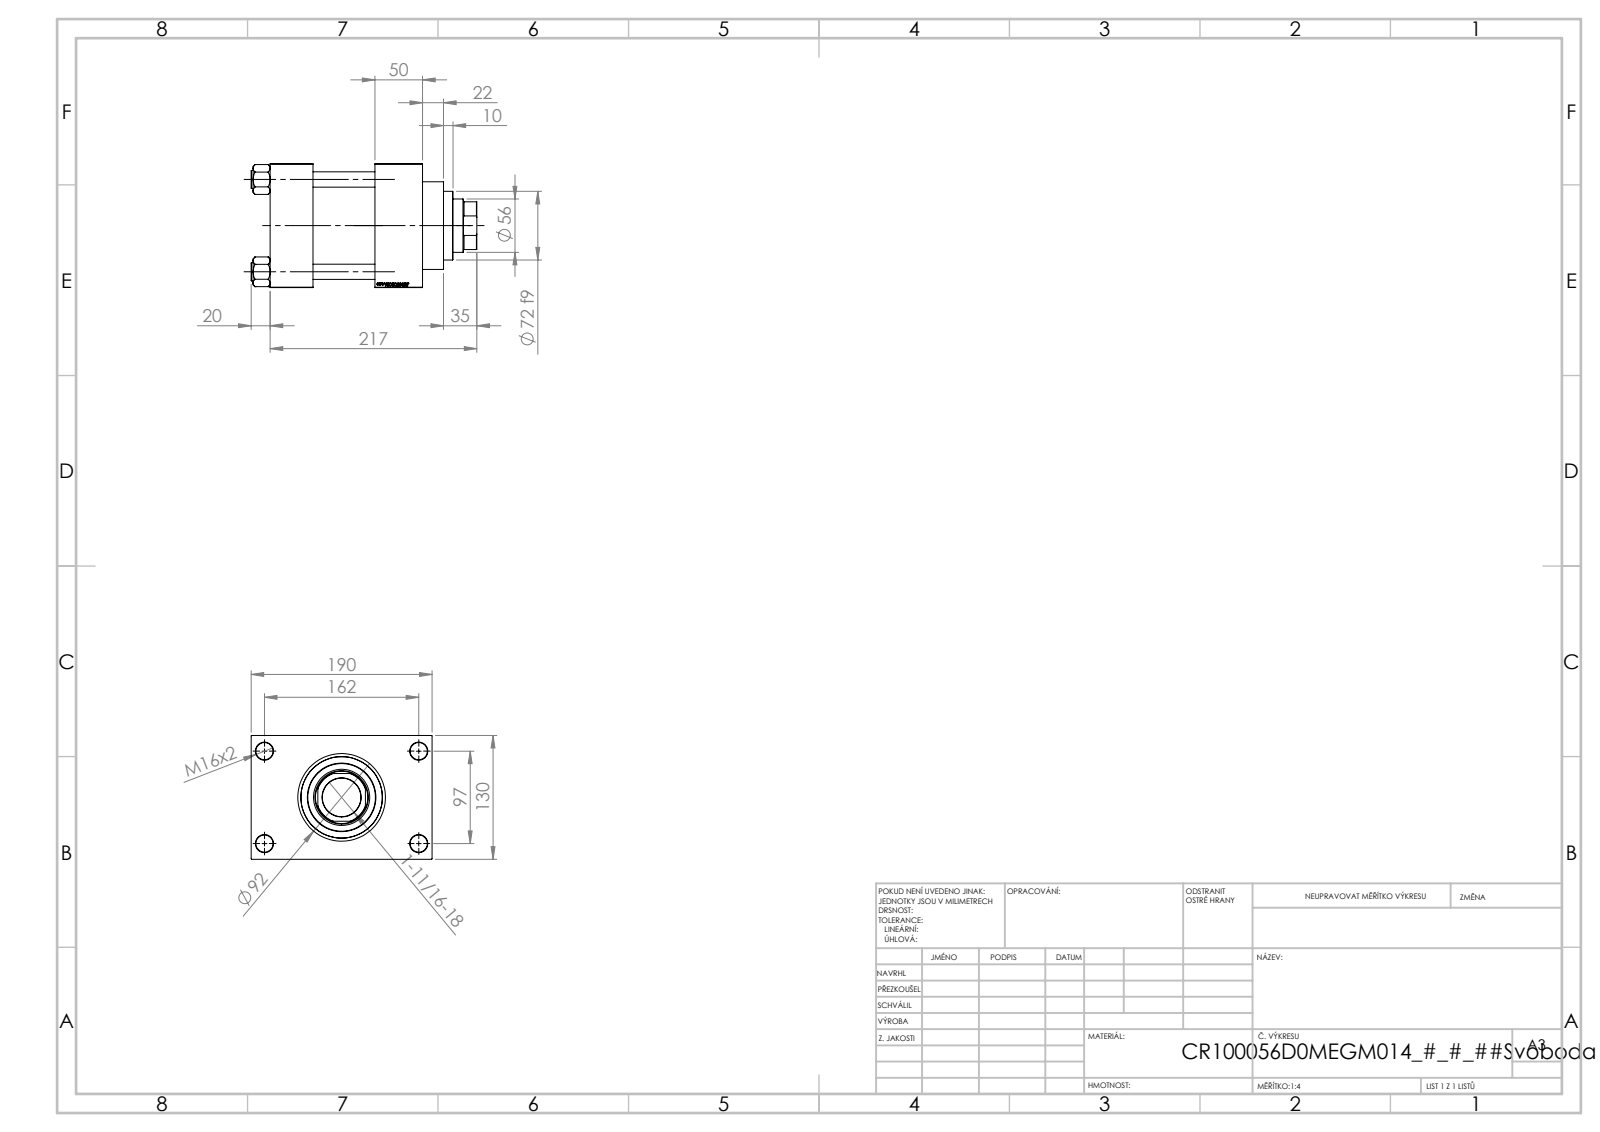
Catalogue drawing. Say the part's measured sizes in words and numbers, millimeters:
The part is named "V215CR_VCP_D; NUT_M5_D; V215_VC_A; V215CR_D_Body (+1 more)". Its 3-D file was written by "SolidWorks 2019 (CONFIG_CONTROL_DESIGN)". It is 11 solids with 1152 faces: 545 planar, 89 cylindrical and 518 other. Overall it measures 237 by 190 by 130 millimeters. Its volume is 2 619 000 cubic millimeters and its surface area 353 729 square millimeters. Round holes: 4 of diameter 16, 4 of diameter 18, 2 of diameter 7, 2 of diameter 26.44, 2 of diameter 35, 1 of diameter 40.5, 1 of diameter 56, 1 of diameter 59, 1 of diameter 76, 1 of diameter 85.5, 1 of diameter 100. Round bosses or shafts: 4 of diameter 19, 1 of diameter 106, 1 of diameter 92, 1 of diameter 72. Partial cylindrical surfaces (rounded edges, fillets, slot ends): 1 of radius 27. The main face-to-face distances are 160, 130, 65, 50, 45, 110, 115, 30, 96, 190. The hole center spacings are 32.55, 68.52, 94.41, 96.9, 102.27, 129.45, 161.73, 97.
